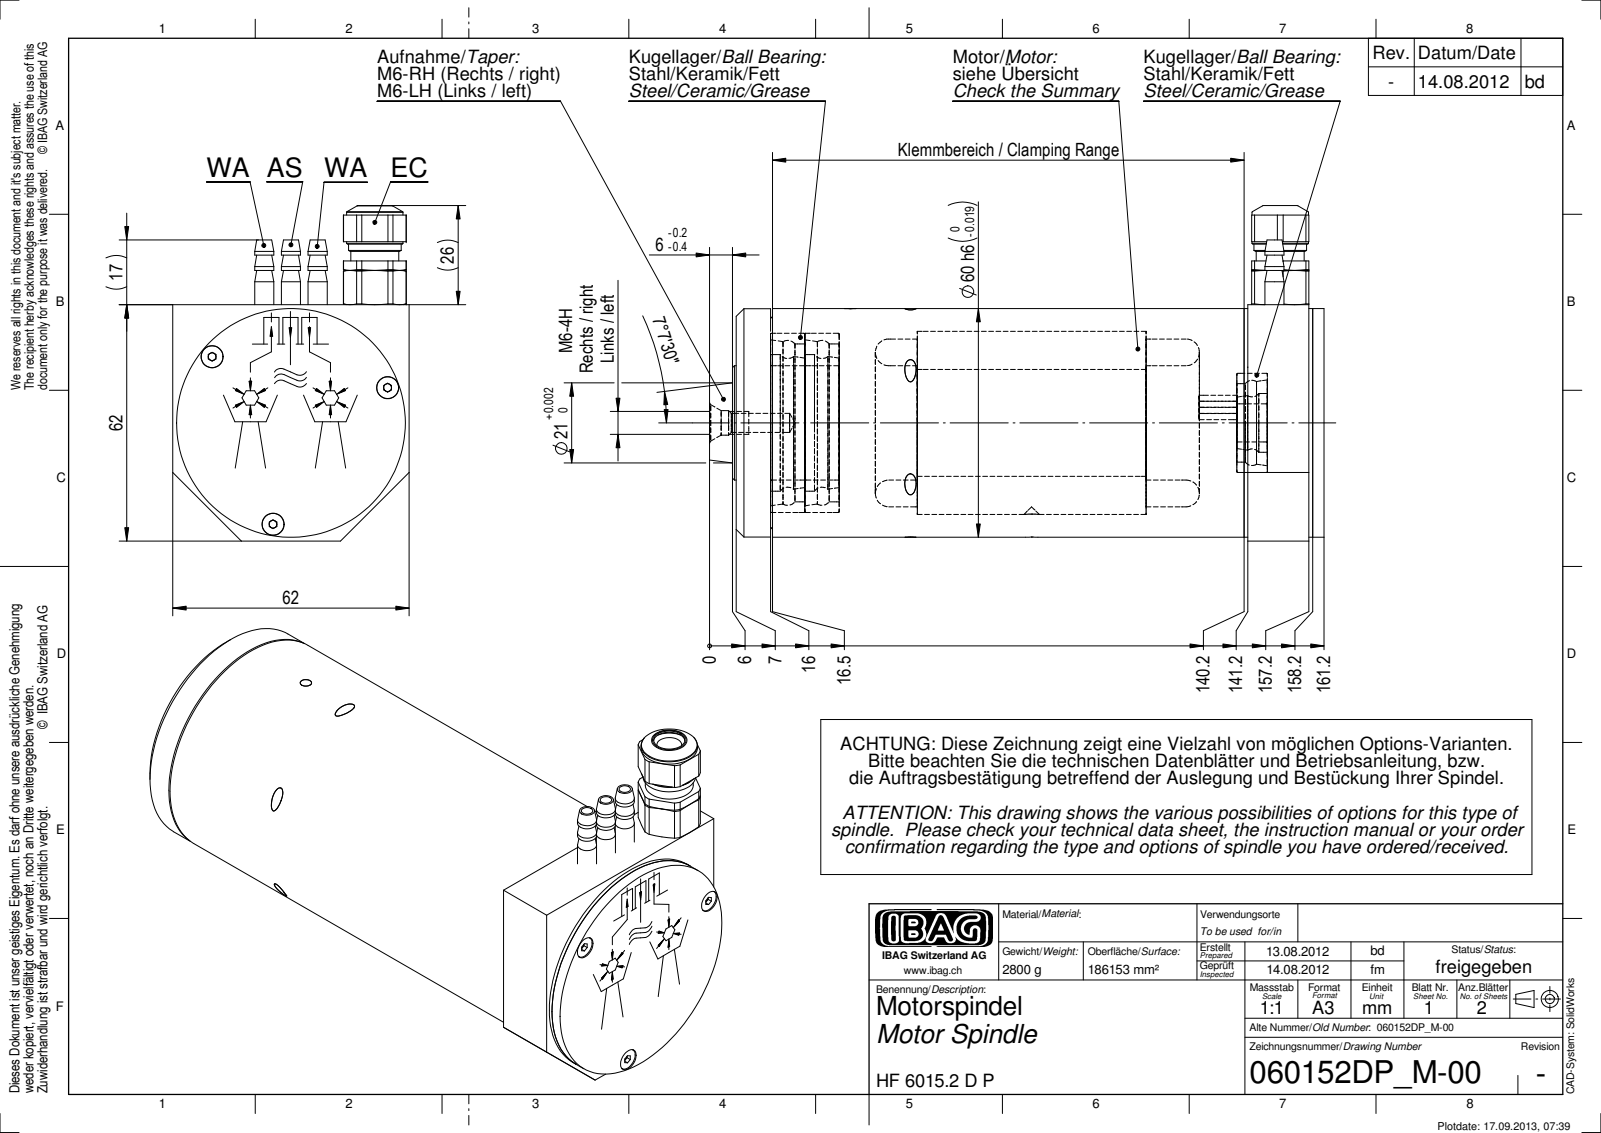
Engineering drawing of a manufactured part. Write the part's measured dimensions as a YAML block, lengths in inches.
part_name: "060152DP_M-00"
step_written_by: "SolidWorks 2012 (CONFIG_CONTROL_DESIGN)"
units: inches
bodies: {solids: 0, faces: 230, planar: 71, cylindrical: 95, other: 64}
overall_size: [6.346, 3.465, 2.441]
round_holes:
  - {diameter: 0.118, count: 7}
  - {diameter: 0.228, count: 3}
  - {diameter: 0.13, count: 1}
  - {diameter: 0.252, count: 1}
  - {diameter: 0.256, count: 1}
  - {diameter: 0.323, count: 1}
round_bosses_or_shafts:
  - {diameter: 0.197, count: 3}
  - {diameter: 0.118, count: 2}
  - {diameter: 2.362, count: 1}
  - {diameter: 2.358, count: 1}
  - {diameter: 1.181, count: 1}
  - {diameter: 0.583, count: 1}
  - {diameter: 0.543, count: 1}
  - {diameter: 0.496, count: 1}
partial_cylinders:
  - {radius: 0.325, count: 1}
face_to_face_distances: [0.039, 6.071, 0.669, 5.953, 2.441, 0.63, 5.283, 0.118, 0.157, 5.244]
hole_center_spacings: [0.805, 1.139, 1.063, 0.276, 1.61, 1.841, 2.523, 0.304]
